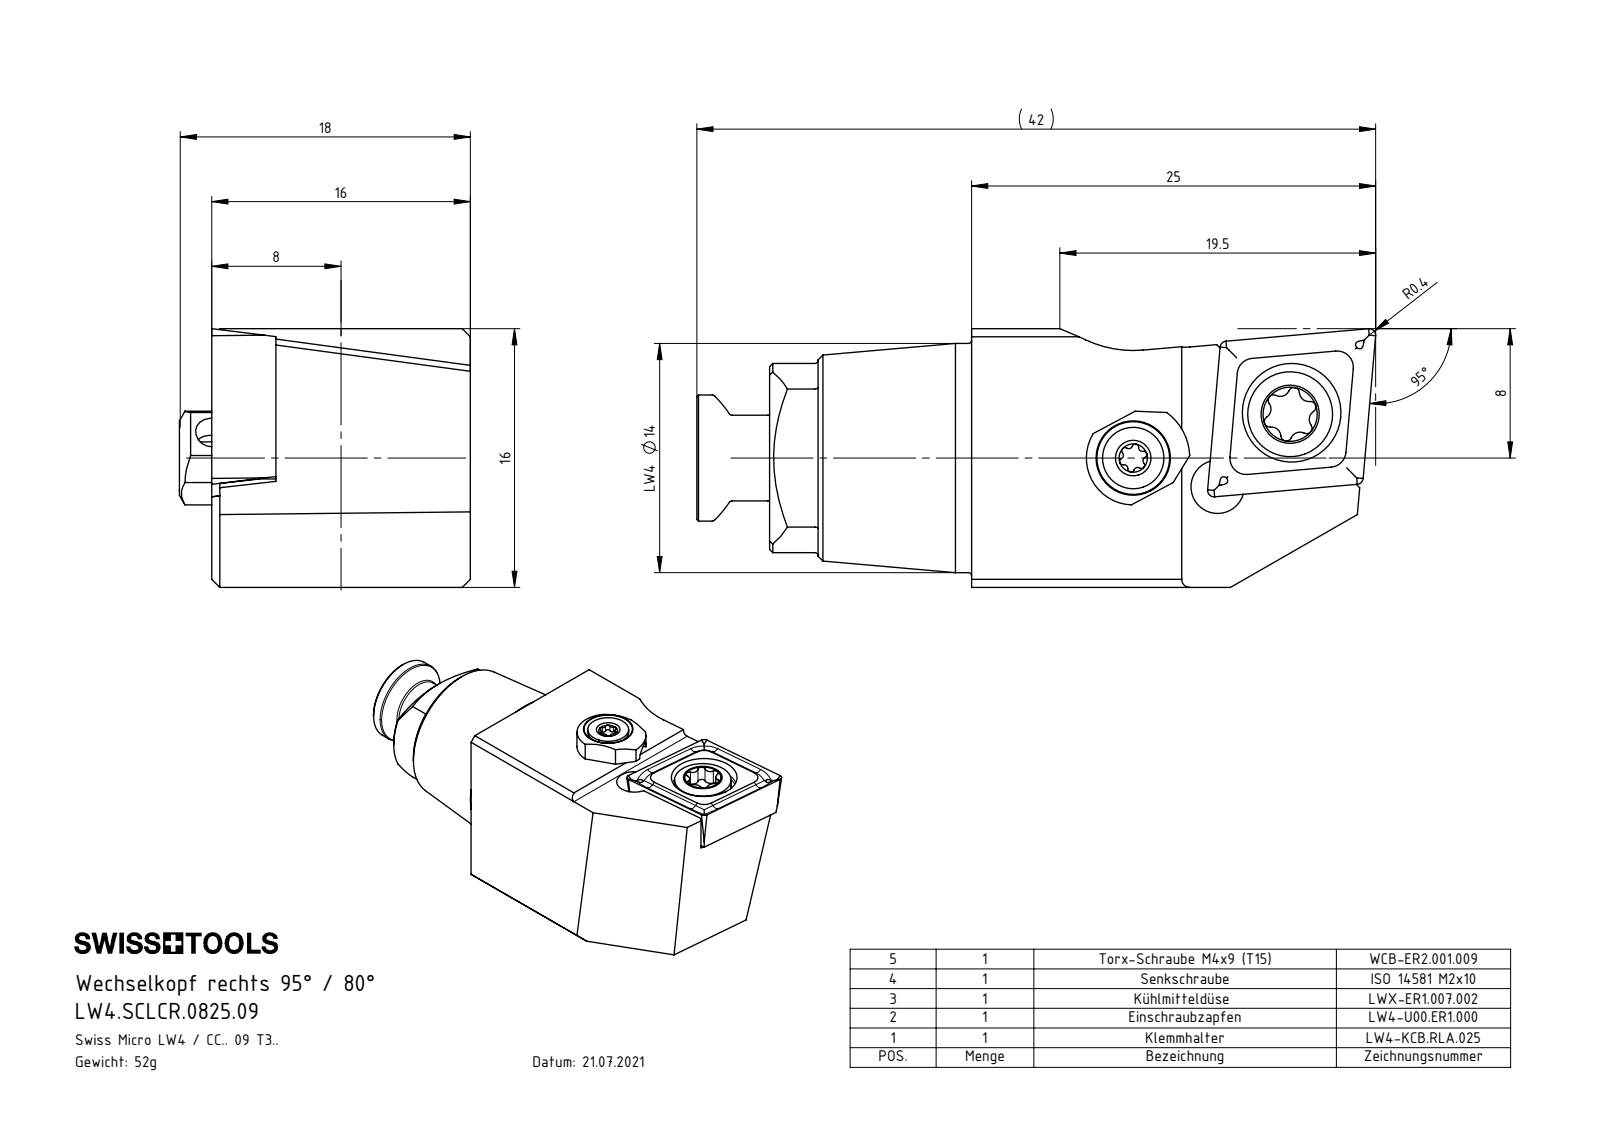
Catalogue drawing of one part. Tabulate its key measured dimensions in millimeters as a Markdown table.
| quantity | value |
| --- | --- |
| part name | ISO 14581 - M2x10; LW4.KCB.RLA.025; LWX-ER1.007.002; WCB-ER2.001.009_A (+3 more) |
| STEP written by | SolidWorks 2017 (AUTOMOTIVE_DESIGN) |
| units | millimeters |
| bodies | 6 solids, 194 faces (69 planar, 53 cylindrical, 72 other) |
| overall size | 42 × 18 × 16 |
| volume | 6 658 mm³ |
| surface area | 3 866 mm² |
| round holes (diameter × count) | 3 × 2, 3.3 × 2, 1.6 × 1, 2 × 1, 2.5 × 1, 4.4 × 1, 5.5 × 1, 6.1 × 1 |
| round bosses / shafts (diameter × count) | 14.17 × 1, 7.7 × 1, 6 × 1, 5.3 × 1, 5.25 × 1, 5 × 1, 4 × 1, 3.8 × 1 |
| partial cylindrical surfaces (radius × count) | 0.2 × 8, 0.24 × 6, 0.34 × 6, 0.59 × 6, 0.5 × 1, 1 × 1, 2.9 × 1, 3.5 × 1 |
| main face-to-face distances | 16, 12.03, 3.97, 15.5, 3.47, 0.5, 7.5, 2, 3, 12.5 |
| hole center spacings | 5.52, 6.35, 6.48, 10.08, 10.19 |
